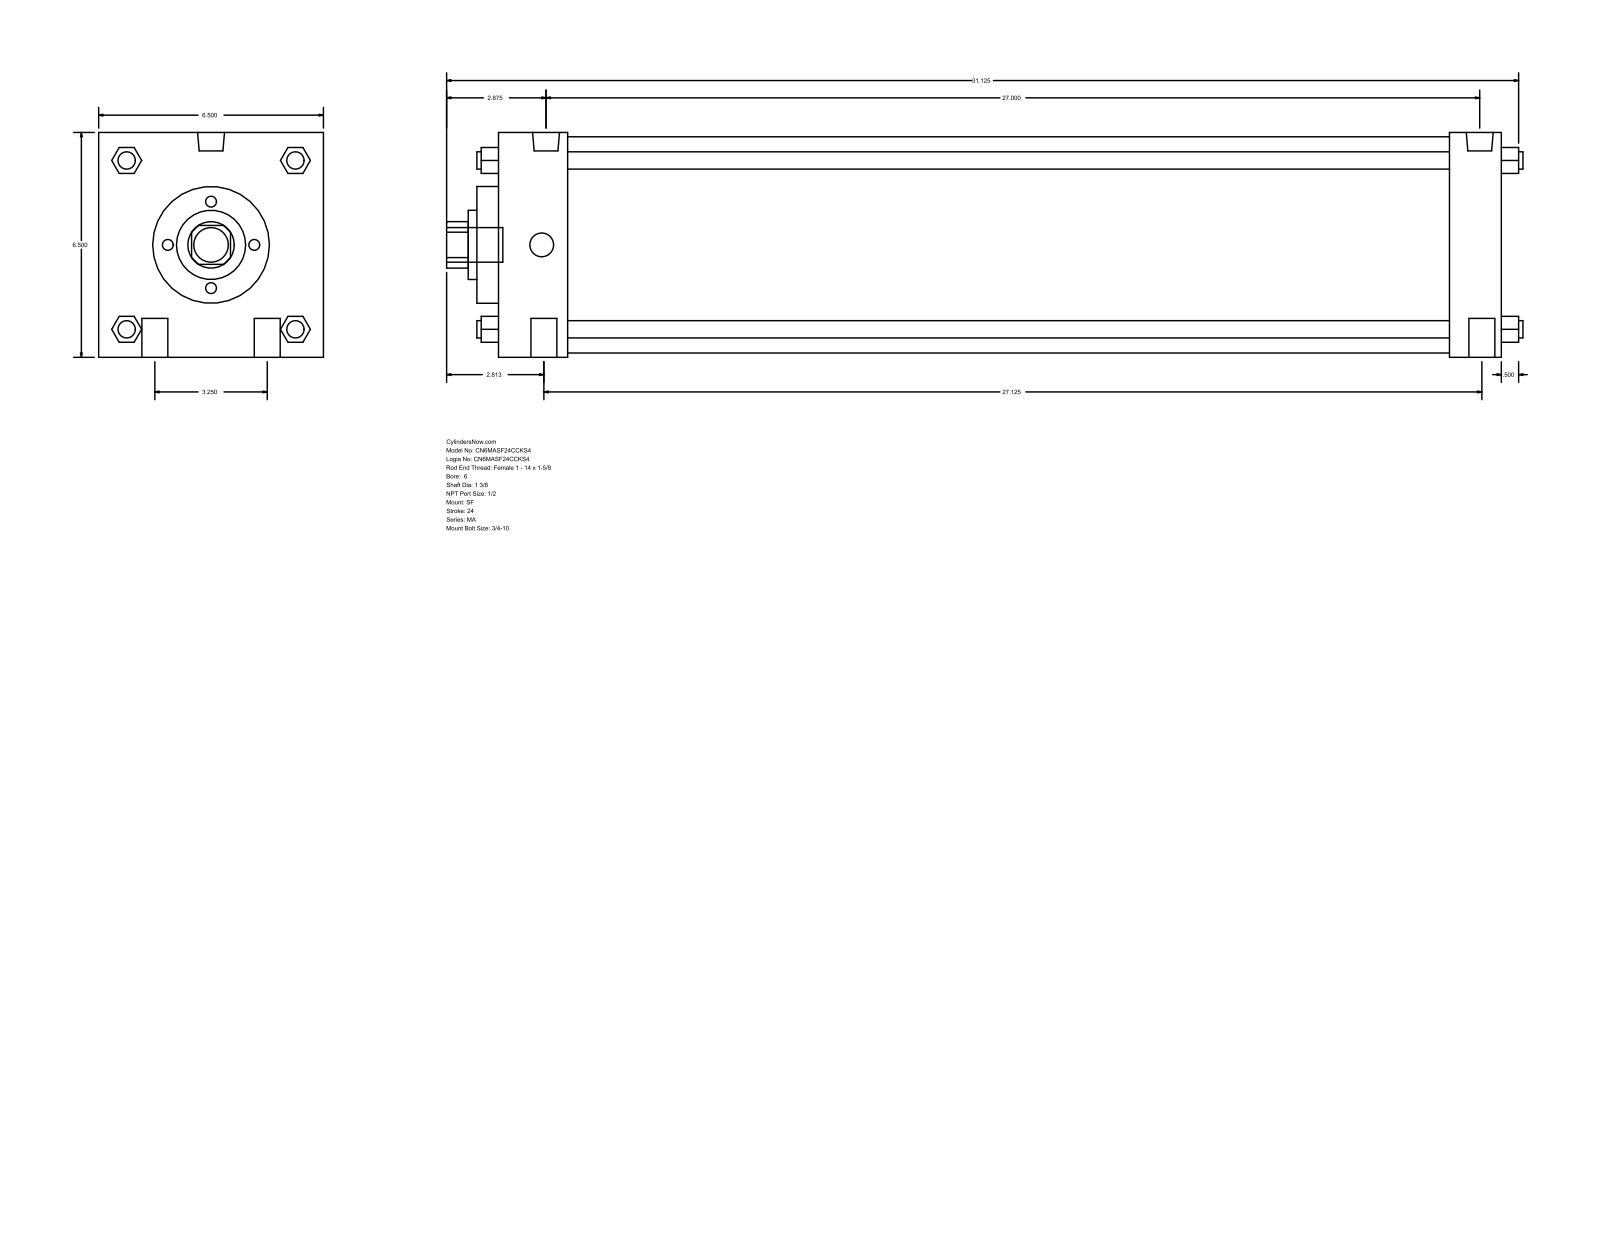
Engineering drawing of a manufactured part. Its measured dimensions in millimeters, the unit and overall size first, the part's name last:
Units: millimetres
Overall size (bounding box): 790.58 × 165.1 × 165.1
Round holes (diameter × count): ⌀34.92 ×1, ⌀50.8 ×1, ⌀85.72 ×1, ⌀158.75 ×1
Round bosses / shafts (diameter × count): ⌀19.05 ×4, ⌀12.7 ×4, ⌀19.77 ×2, ⌀17.46 ×2, ⌀25.4 ×1
Partial cylindrical surfaces — rounded edges, fillets, slot ends (radius × count): R17.06 ×1
Main face-to-face distances: 165.1, 736.6, 698.5, 50.8, 38.1, 647.7, 685.8, 15.87, 66.67, 714.37
Bodies: 0 solids, 126 faces (95 planar, 31 cylindrical, 0 other)
Part name (STEP PRODUCT): MA_SF__0600_1.375
STEP written by: GSSL Pune (CONFIG_CONTROL_DESIGN)
